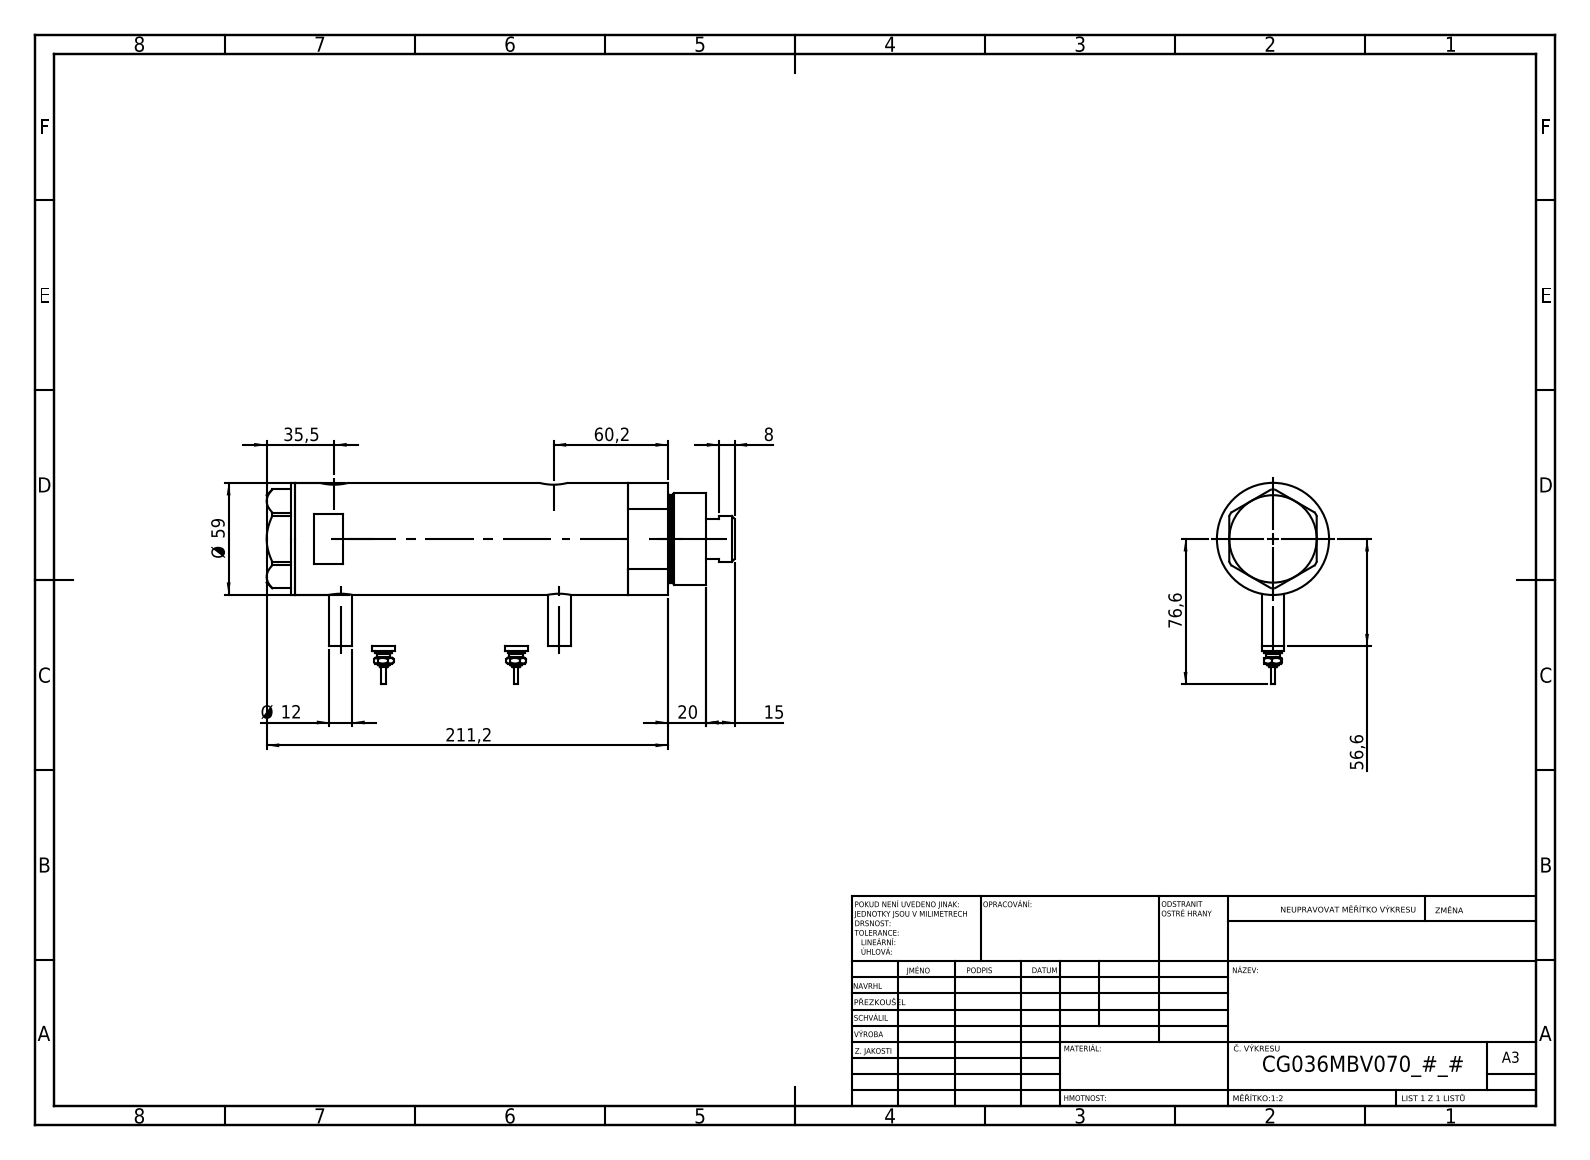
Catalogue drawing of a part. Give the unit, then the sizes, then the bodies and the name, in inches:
Units: inches
Overall size (bounding box): 9.693 × 4.177 × 2.323
Round holes (diameter × count): ⌀0.383 ×2, ⌀0.492 ×2, ⌀0.591 ×2, ⌀0.335 ×1, ⌀0.984 ×1, ⌀1.043 ×1, ⌀1.417 ×1, ⌀1.575 ×1, ⌀2.047 ×1
Round bosses / shafts (diameter × count): ⌀0.472 ×4, ⌀0.354 ×2, ⌀0.276 ×2, ⌀0.177 ×2, ⌀0.098 ×2, ⌀2.323 ×1, ⌀1.89 ×1, ⌀1.811 ×1
Main face-to-face distances: 5.402, 0.925, 4.476, 0.591, 1.516, 5.992, 0.079, 9.102, 8.512, 7.587
Hole centre spacings: 0.114, 0.138, 4.409, 4.524, 4.547, 4.661
Volume: 34.76 in³ · Surface area: 180.5 in²
Bodies: 6 solids, 212 faces (79 planar, 69 cylindrical, 64 other)
Part name (STEP PRODUCT): Switch; V270CG_BACK; V270CG_MIDDLE; V270CG_FRONT (+1 more)
STEP written by: SolidWorks 2019 (CONFIG_CONTROL_DESIGN)
